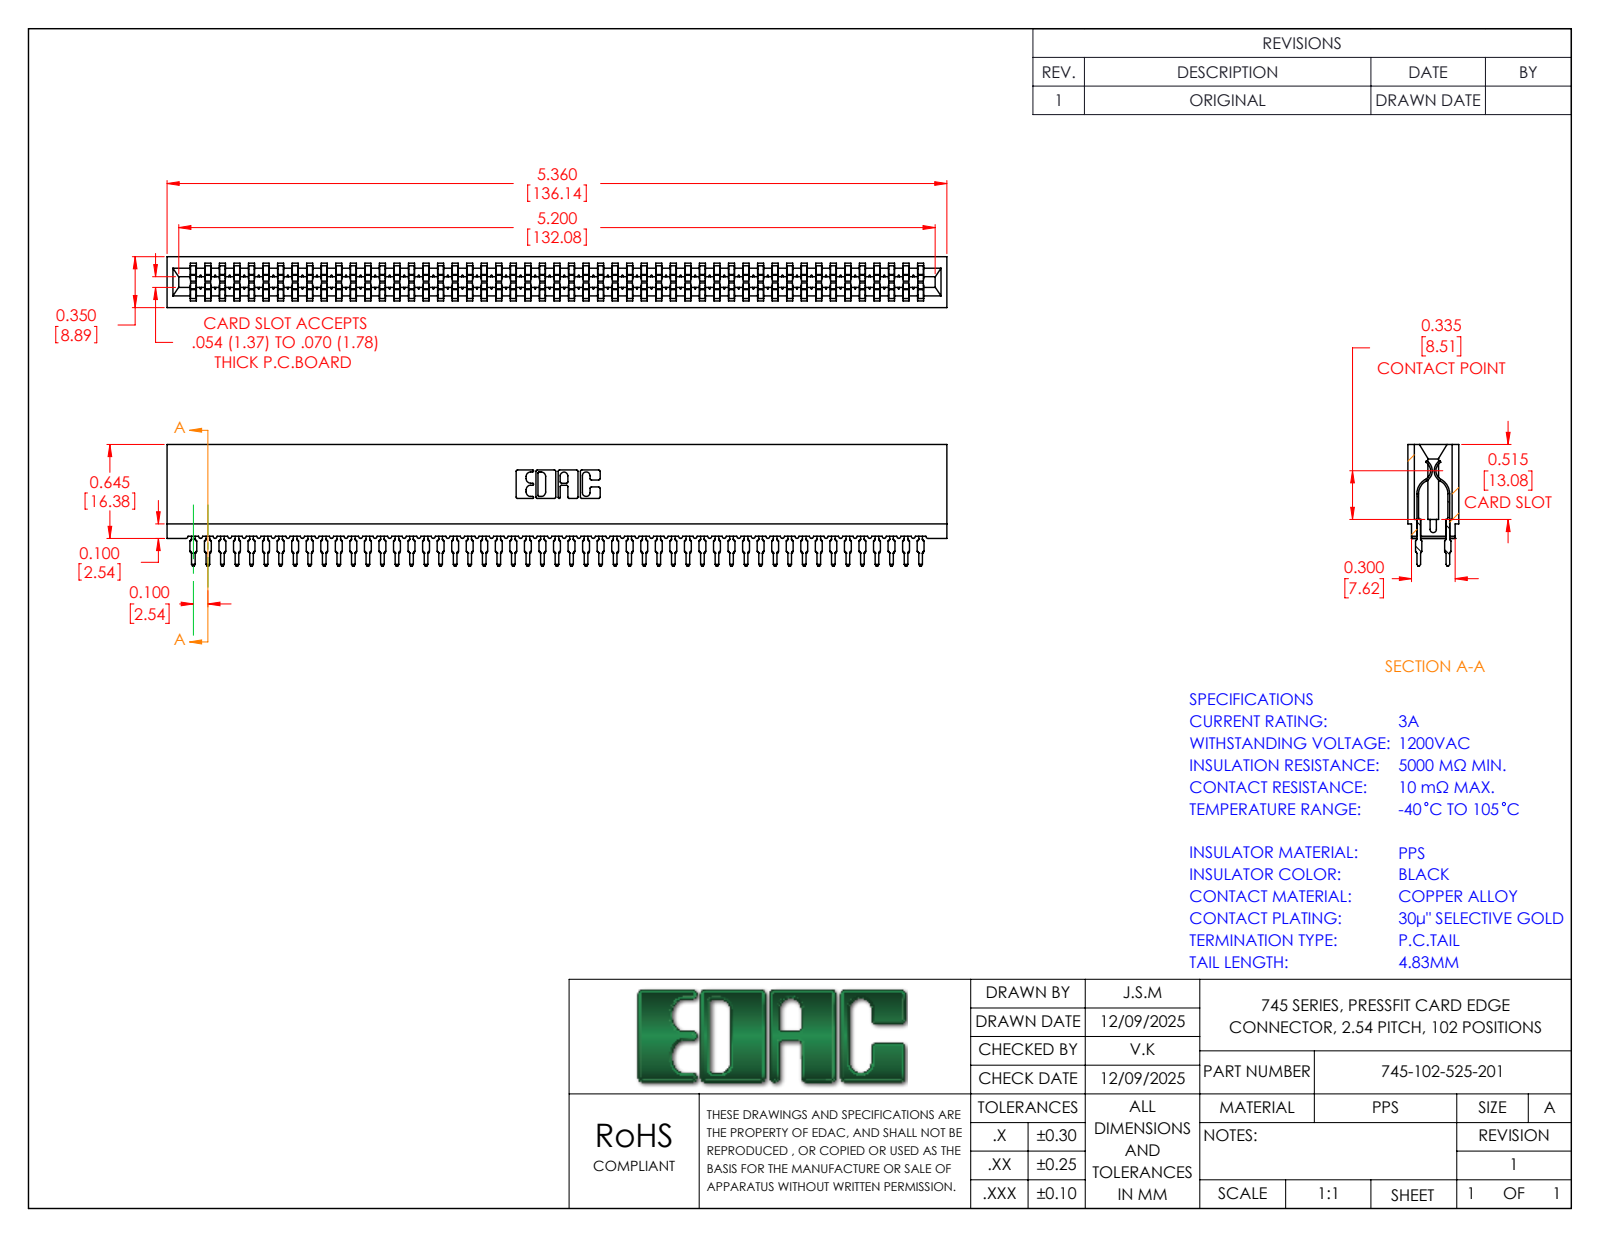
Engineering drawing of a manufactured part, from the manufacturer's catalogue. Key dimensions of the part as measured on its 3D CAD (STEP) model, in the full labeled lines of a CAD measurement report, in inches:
Part name (STEP PRODUCT): 745-102-525-201; 745 Part_Insulator Option - 01; 745-292-001_525
STEP written by: SolidWorks 2023 (CONFIG_CONTROL_DESIGN)
Units: inches
Bodies: 103 solids, 9224 faces (4747 planar, 1825 cylindrical, 2652 other)
Overall size (bounding box): 5.36 × 0.835 × 0.35
Volume: 0.743 in³ · Surface area: 38.55 in²
Partial cylindrical surfaces — rounded edges, fillets, slot ends (radius × count): R0.022 ×204, R0.015 ×102, R0.01 ×22, R0.005 ×8, R0.011 ×8, R0.007 ×6, R0.031 ×6, R0.026 ×3
Main face-to-face distances: 0.35, 0.063, 0.287, 0.045, 0.305, 0.018, 0.243, 0.138, 0.212, 0.093
